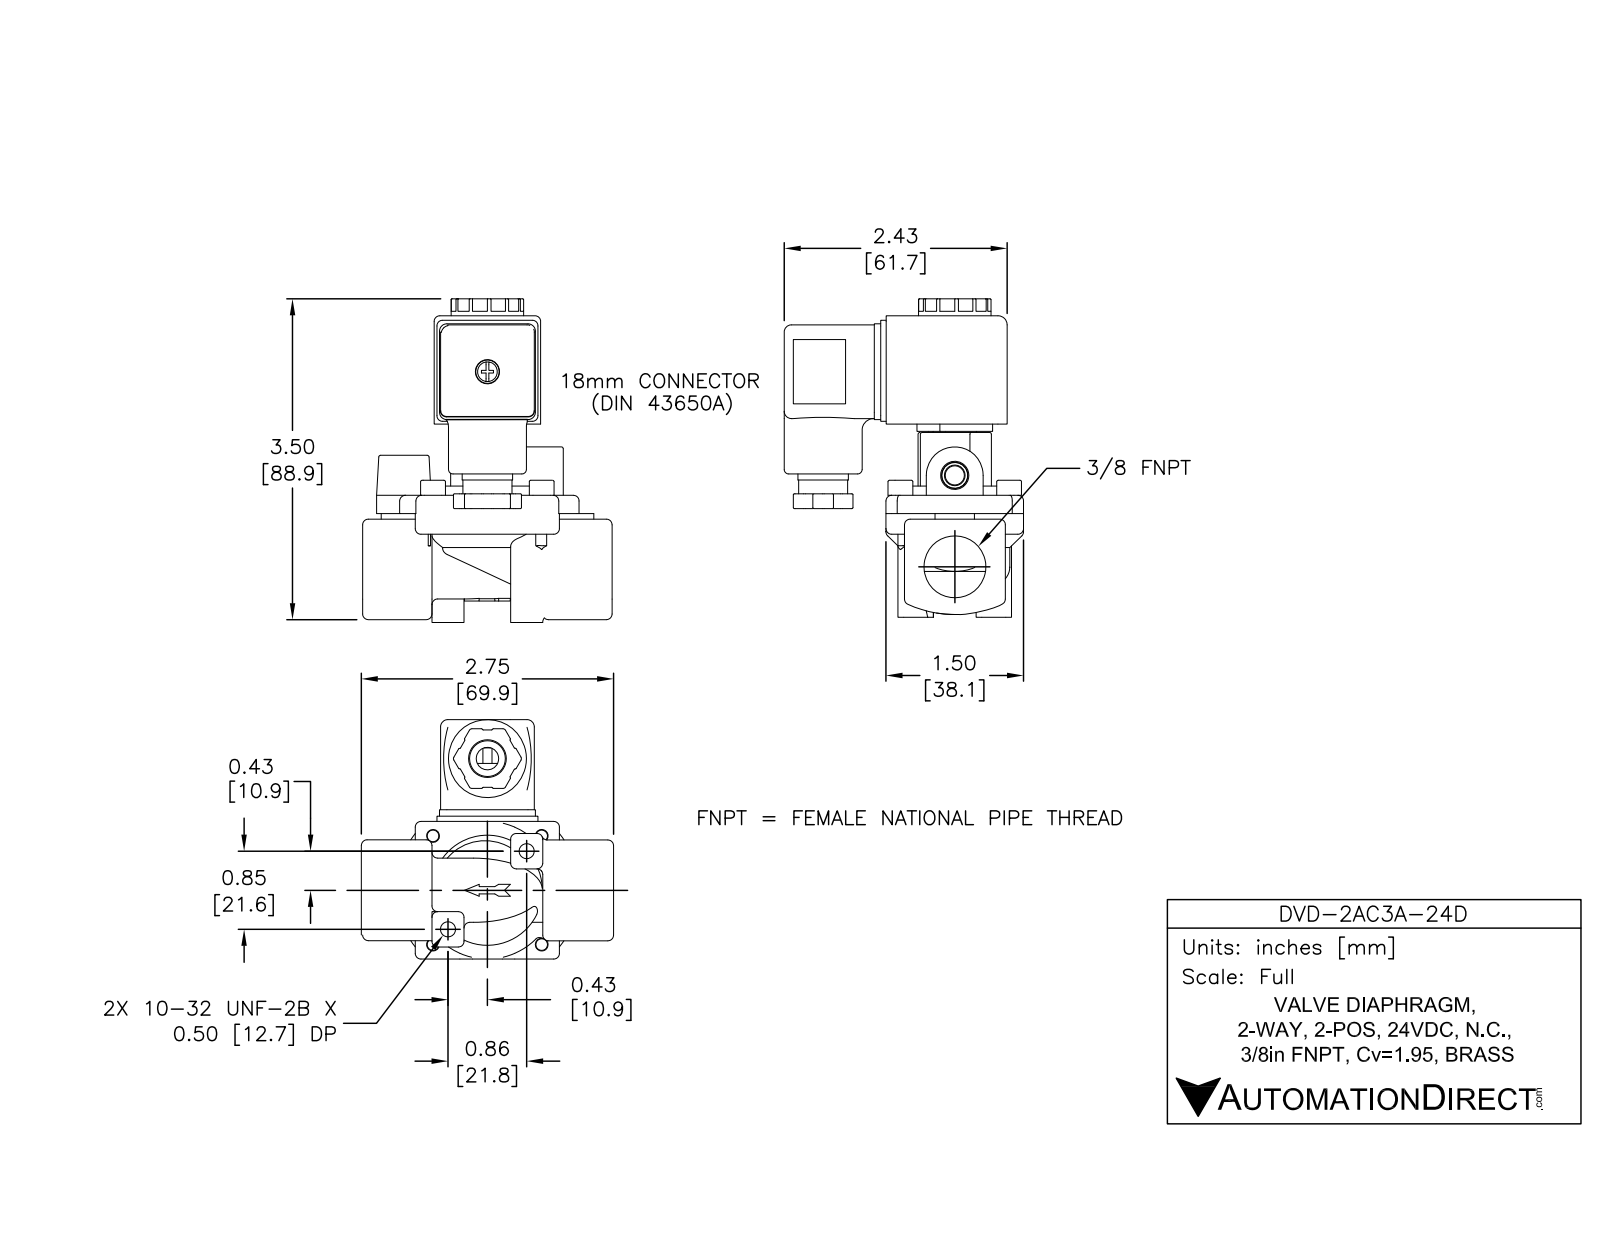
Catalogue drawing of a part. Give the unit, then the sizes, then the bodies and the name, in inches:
Units: inches
Overall size (bounding box): 3.439 × 2.722 × 2.62
Round holes (diameter × count): ⌀0.13 ×4, ⌀0.164 ×4, ⌀0.156 ×3, ⌀0.038 ×2, ⌀0.06 ×2, ⌀0.098 ×2, ⌀0.14 ×2, ⌀0.5 ×2, ⌀0.062 ×1, ⌀0.077 ×1, ⌀0.089 ×1, ⌀0.093 ×1
Round bosses / shafts (diameter × count): ⌀0.27 ×4, ⌀0.177 ×4, ⌀0.16 ×4, ⌀1.375 ×1, ⌀1.37 ×1, ⌀0.85 ×1, ⌀0.79 ×1, ⌀0.609 ×1
Partial cylindrical surfaces — rounded edges, fillets, slot ends (radius × count): R0.01 ×52, R0.062 ×46, R0.031 ×17, R0.08 ×12, R0.156 ×12, R0.05 ×8, R0.03 ×6, R0.062 ×5
Main face-to-face distances: 1.161, 0.925, 0.2, 0.078, 1.1, 1.043, 0.965, 0.257, 1.3, 0.021
Hole centre spacings: 0.924, 0.311, 0.617, 0.838, 1.172, 1.185, 0.747, 0.924
Volume: 5.764 in³ · Surface area: 71.06 in²
Bodies: 8 solids, 1959 faces (871 planar, 435 cylindrical, 653 other)
Part name (STEP PRODUCT): DVD-2AC3A-24D
STEP written by: SolidWorks 2015 (AUTOMOTIVE_DESIGN)
